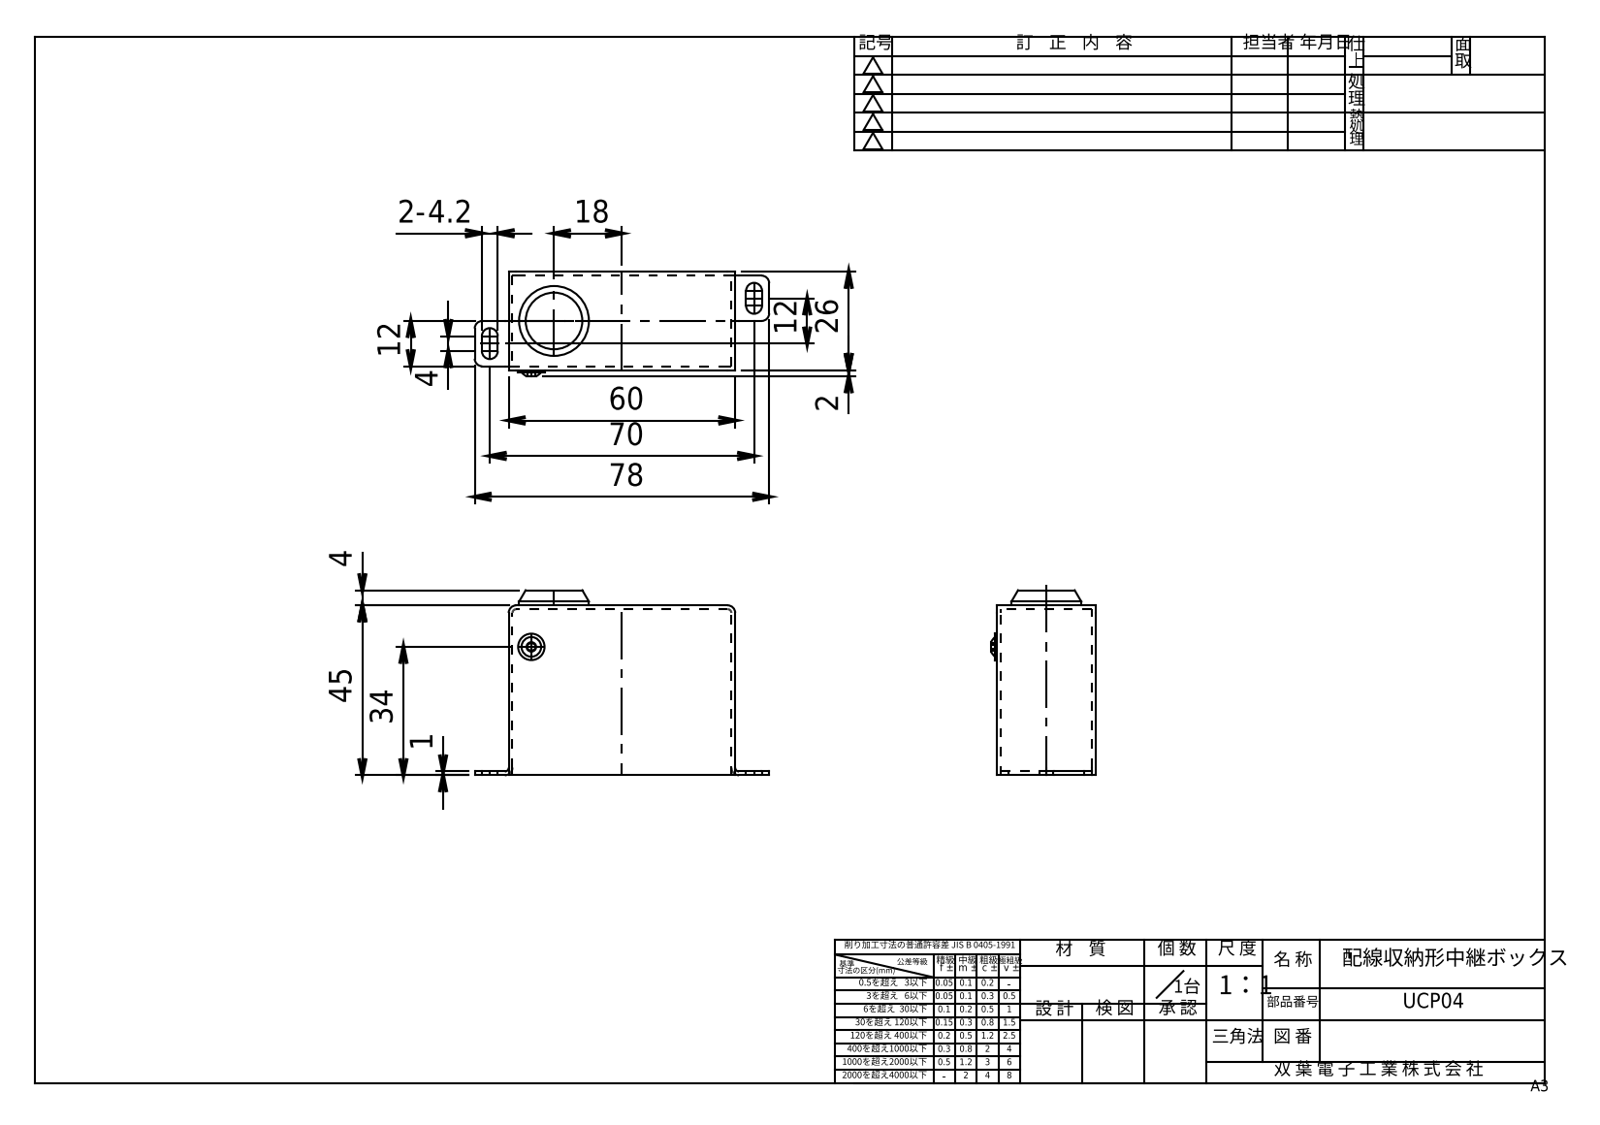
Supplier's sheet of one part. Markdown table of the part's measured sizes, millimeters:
| quantity | value |
| --- | --- |
| STEP written by | XStep 1.0 (automotive_design) |
| units | millimeters |
| bodies | 1 solid, 58 faces (38 planar, 18 cylindrical, 2 other) |
| overall size | 78 × 49 × 27.65 |
| volume | 10 019 mm³ |
| surface area | 18 531 mm² |
| round bosses / shafts (diameter × count) | 18.5 × 1, 7 × 1 |
| partial cylindrical surfaces (radius × count) | 2 × 8, 1 × 4, 2.1 × 4 |
| main face-to-face distances | 1, 25, 26, 24, 59, 60, 58, 44, 45, 5 |
